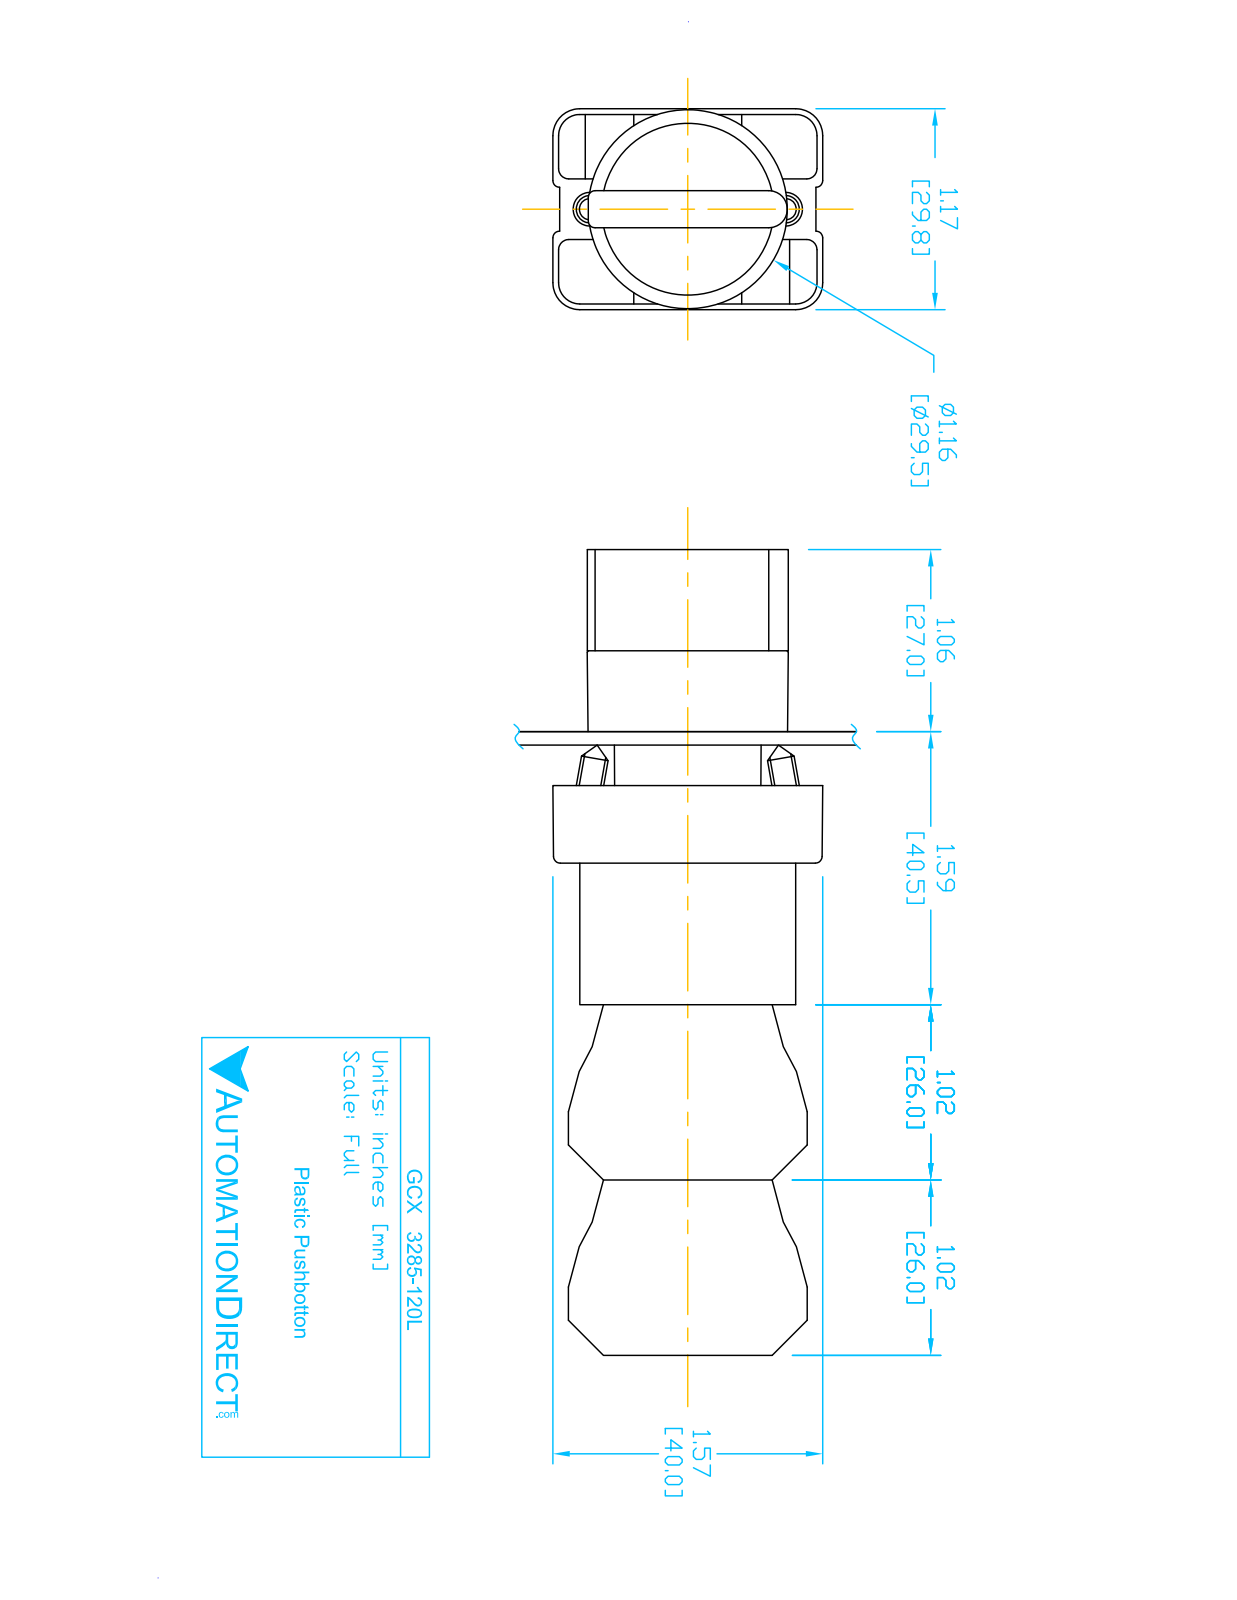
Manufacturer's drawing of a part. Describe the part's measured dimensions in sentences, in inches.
The part is named "ecx1040; ECX3029-2; GCX3285-120L; ecx1030 (+2 more)". Its 3-D file was written by "SolidWorks 2016 (AUTOMOTIVE_DESIGN)". It is 11 solids with 724 faces: 488 planar, 193 cylindrical and 43 other. Overall it measures 4.677 by 1.581 by 1.177 inches. Its volume is 4.751 cubic inches and its surface area 59.22 square inches. Round holes: 4 of diameter 0.079, 2 of diameter 0.087, 2 of diameter 0.124, 2 of diameter 0.13, 1 of diameter 0.197, 1 of diameter 0.469, 1 of diameter 0.878, 1 of diameter 0.888, 1 of diameter 1.024. Round bosses or shafts: 4 of diameter 0.157, 1 of diameter 1.175, 1 of diameter 1.004, 1 of diameter 0.945, 1 of diameter 0.856, 1 of diameter 0.78, 1 of diameter 0.504. Partial cylindrical surfaces (rounded edges, fillets, slot ends): 24 of radius 0.059, 12 of radius 0.041, 12 of radius 0.124, 12 of radius 0.157, 9 of radius 0.039, 2 of radius 0.02, 2 of radius 0.063, 2 of radius 0.079. The main face-to-face distances are 0.579, 0.593, 1.024, 1.171, 0.014, 0.827, 1.85, 3.043, 2.02, 1.193. The hole center spacings are 0.236, 1.003, 0.974, 0.472, 0.539, 0.544, 1.083, 0.484.
